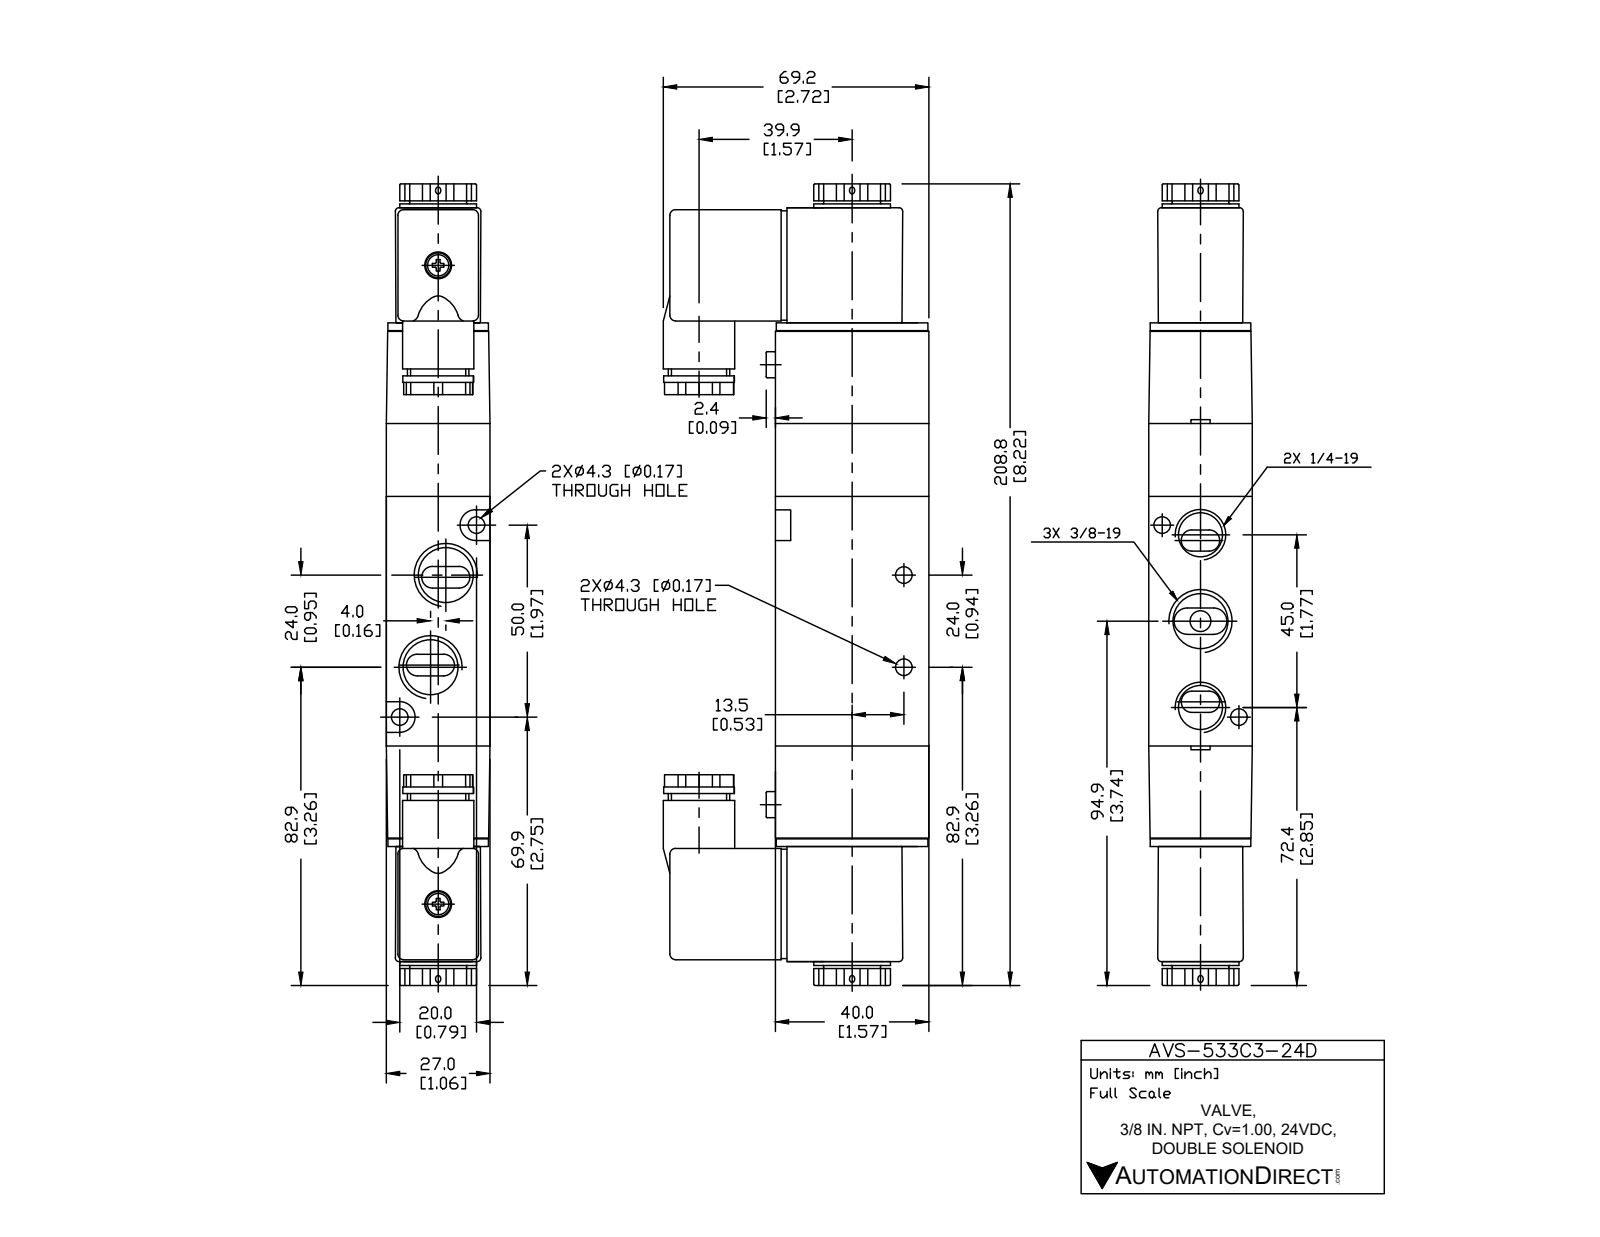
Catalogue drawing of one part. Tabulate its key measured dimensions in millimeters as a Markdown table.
| quantity | value |
| --- | --- |
| part name | AVS-533C3-24D |
| STEP written by | SolidWorks 2015 (CONFIG_CONTROL_DESIGN) |
| units | millimeters |
| bodies | 5 solids, 272 faces (127 planar, 111 cylindrical, 34 other) |
| overall size | 208.8 × 69.2 × 27 |
| volume | 221 817 mm³ |
| surface area | 45 967 mm² |
| round holes (diameter × count) | 4.3 × 4, 14.27 × 3, 11.13 × 2, 9.3 × 1 |
| round bosses / shafts (diameter × count) | 6.7 × 2, 20 × 1, 18.6 × 1, 18.4 × 1, 16 × 1, 14.8 × 1 |
| partial cylindrical surfaces (radius × count) | 1.5 × 18, 3 × 12, 1 × 10, 0.5 × 8 |
| main face-to-face distances | 27, 3, 24, 40, 84, 23.22, 21, 29.5, 0.5, 166.4 |
| hole center spacings | 10.31, 10.69, 12.17, 15.26, 22.5, 26.93, 34.56, 38.9 |
